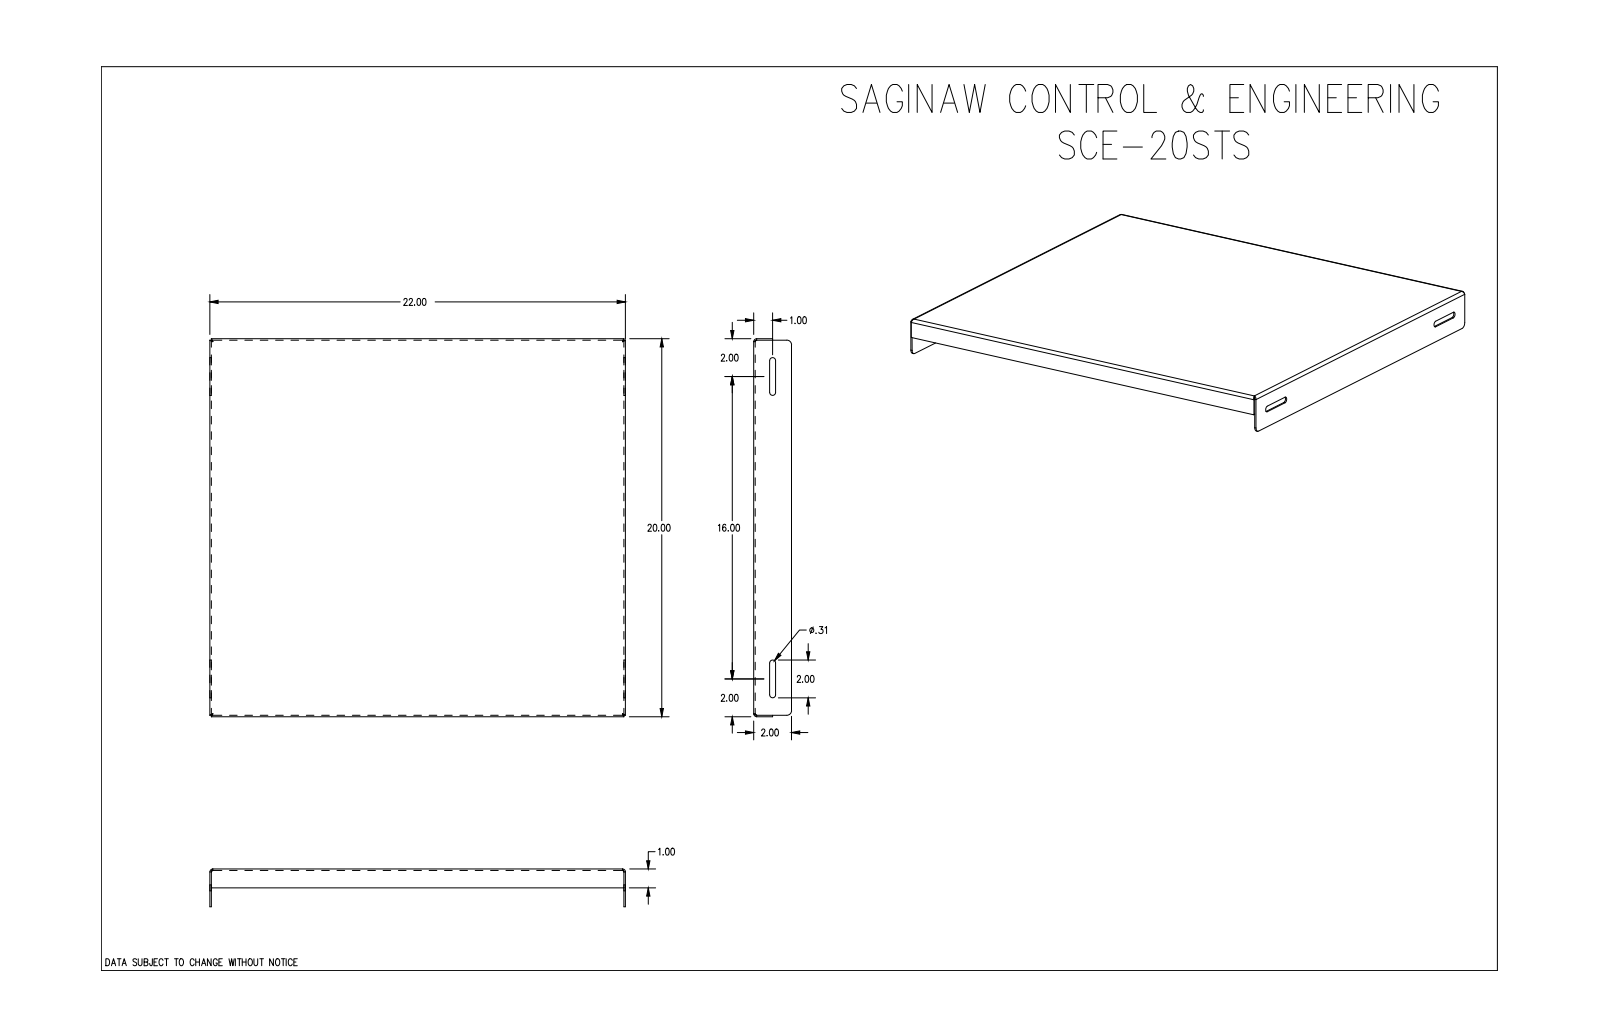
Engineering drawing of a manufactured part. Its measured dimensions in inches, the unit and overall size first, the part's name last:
Units: inches
Overall size (bounding box): 22 × 20 × 2
Partial cylindrical surfaces — rounded edges, fillets, slot ends (radius × count): R0.078 ×4, R0.156 ×4, R0.156 ×4, R0.02 ×2, R0.25 ×2
Main face-to-face distances: 0.078, 21.922, 19.922, 21.844, 22, 19.844, 20, 1, 0.922, 1.922
Volume: 42.89 in³ · Surface area: 1 108 in²
Bodies: 1 solid, 62 faces (30 planar, 24 cylindrical, 8 other)
Part name (STEP PRODUCT): SCE-20STS
STEP written by: SolidWorks 2019 (CONFIG_CONTROL_DESIGN)
